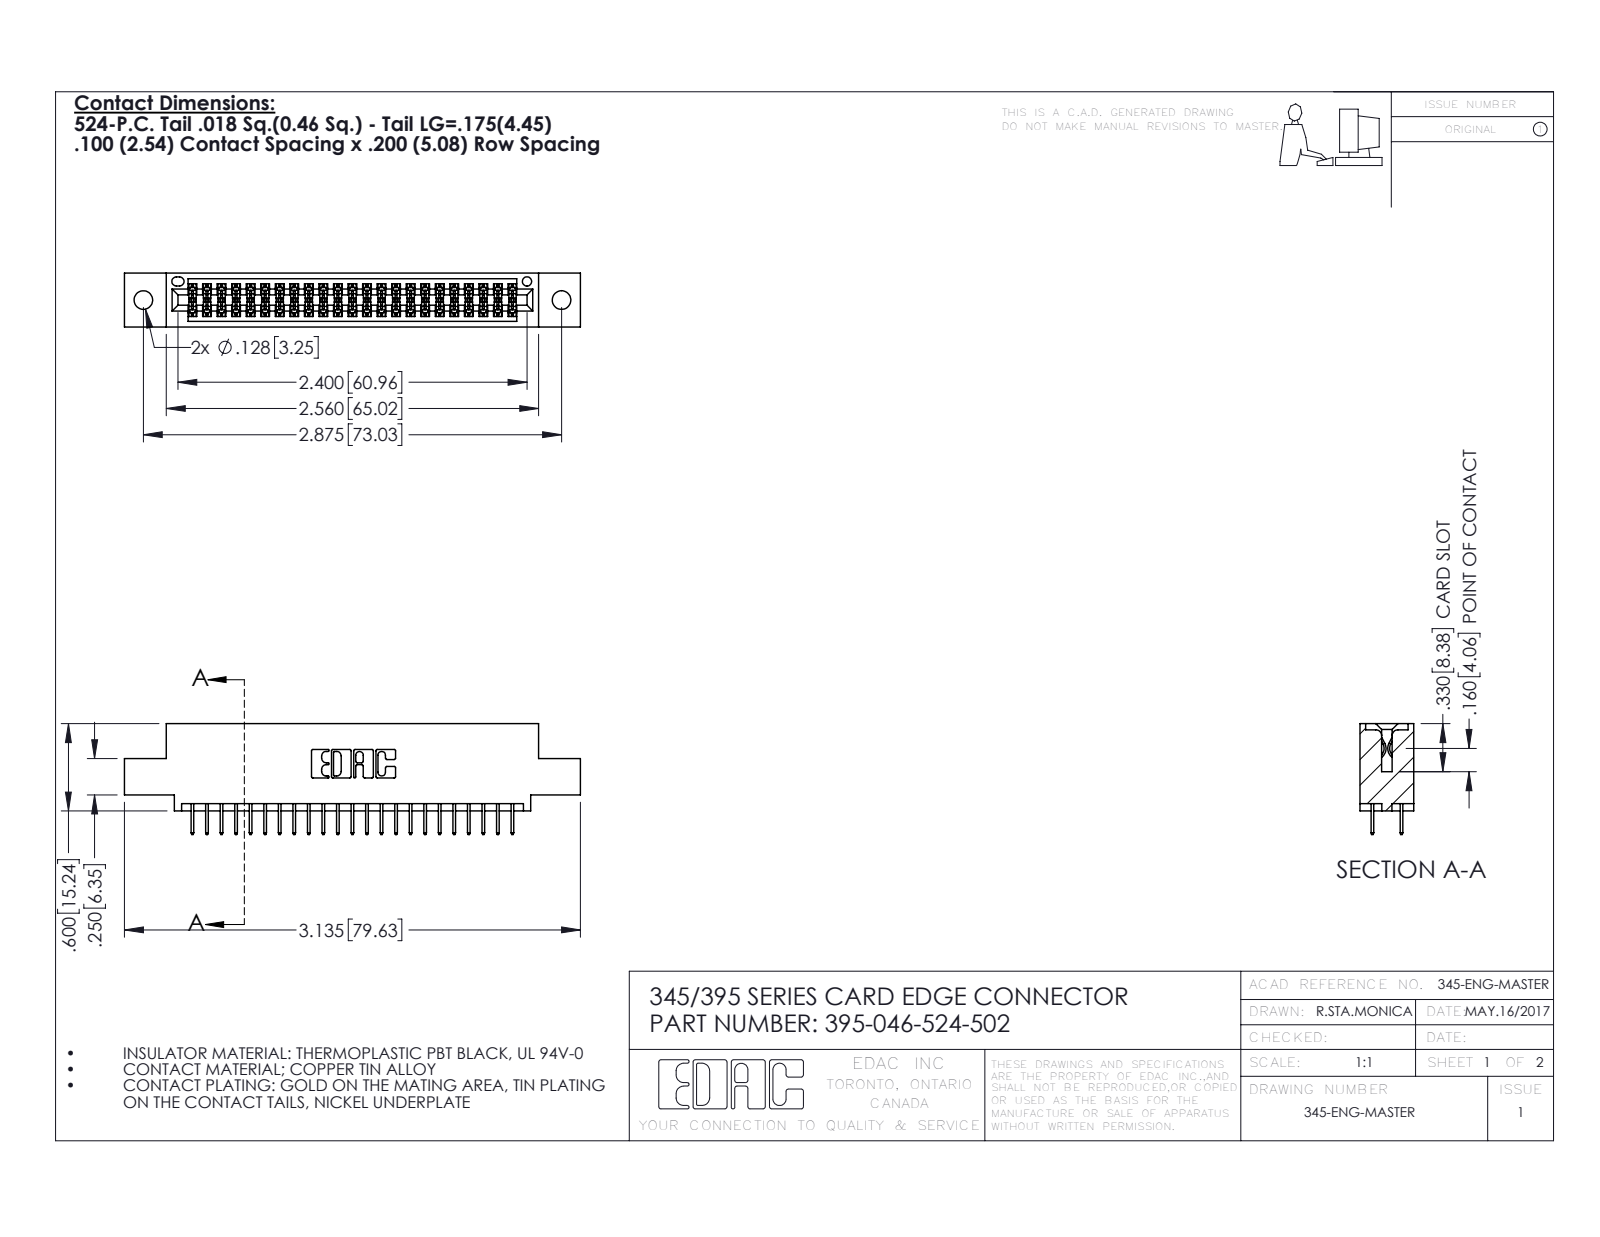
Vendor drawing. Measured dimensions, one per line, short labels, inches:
name: 395-046-524-502; 345 Part_0.110 Offset - 0.128 Dia; 345-292-001_345-293-124
written by: SolidWorks 2016 (CONFIG_CONTROL_DESIGN)
unit: in
bodies: 47 solids, 2614 faces (1878 planar, 736 cylindrical, 0 other)
size: 3.135 × 0.762 × 0.37
volume: 0.45 in³; area: 15.77 in²
holes: 2× ⌀0.128, 1× ⌀0.064
rounds: 69× R0.006, 22× R0.01, 6× R0.007, 6× R0.031, 3× R0.026, 2× R0.014, 2× R0.019, 2× R0.022
face distances: 0.072, 0.298, 0.2, 0.37, 0.098, 0.272, 0.025, 0.225, 0.072, 0.175
hole spacings: 0.27, 2.641, 2.875
